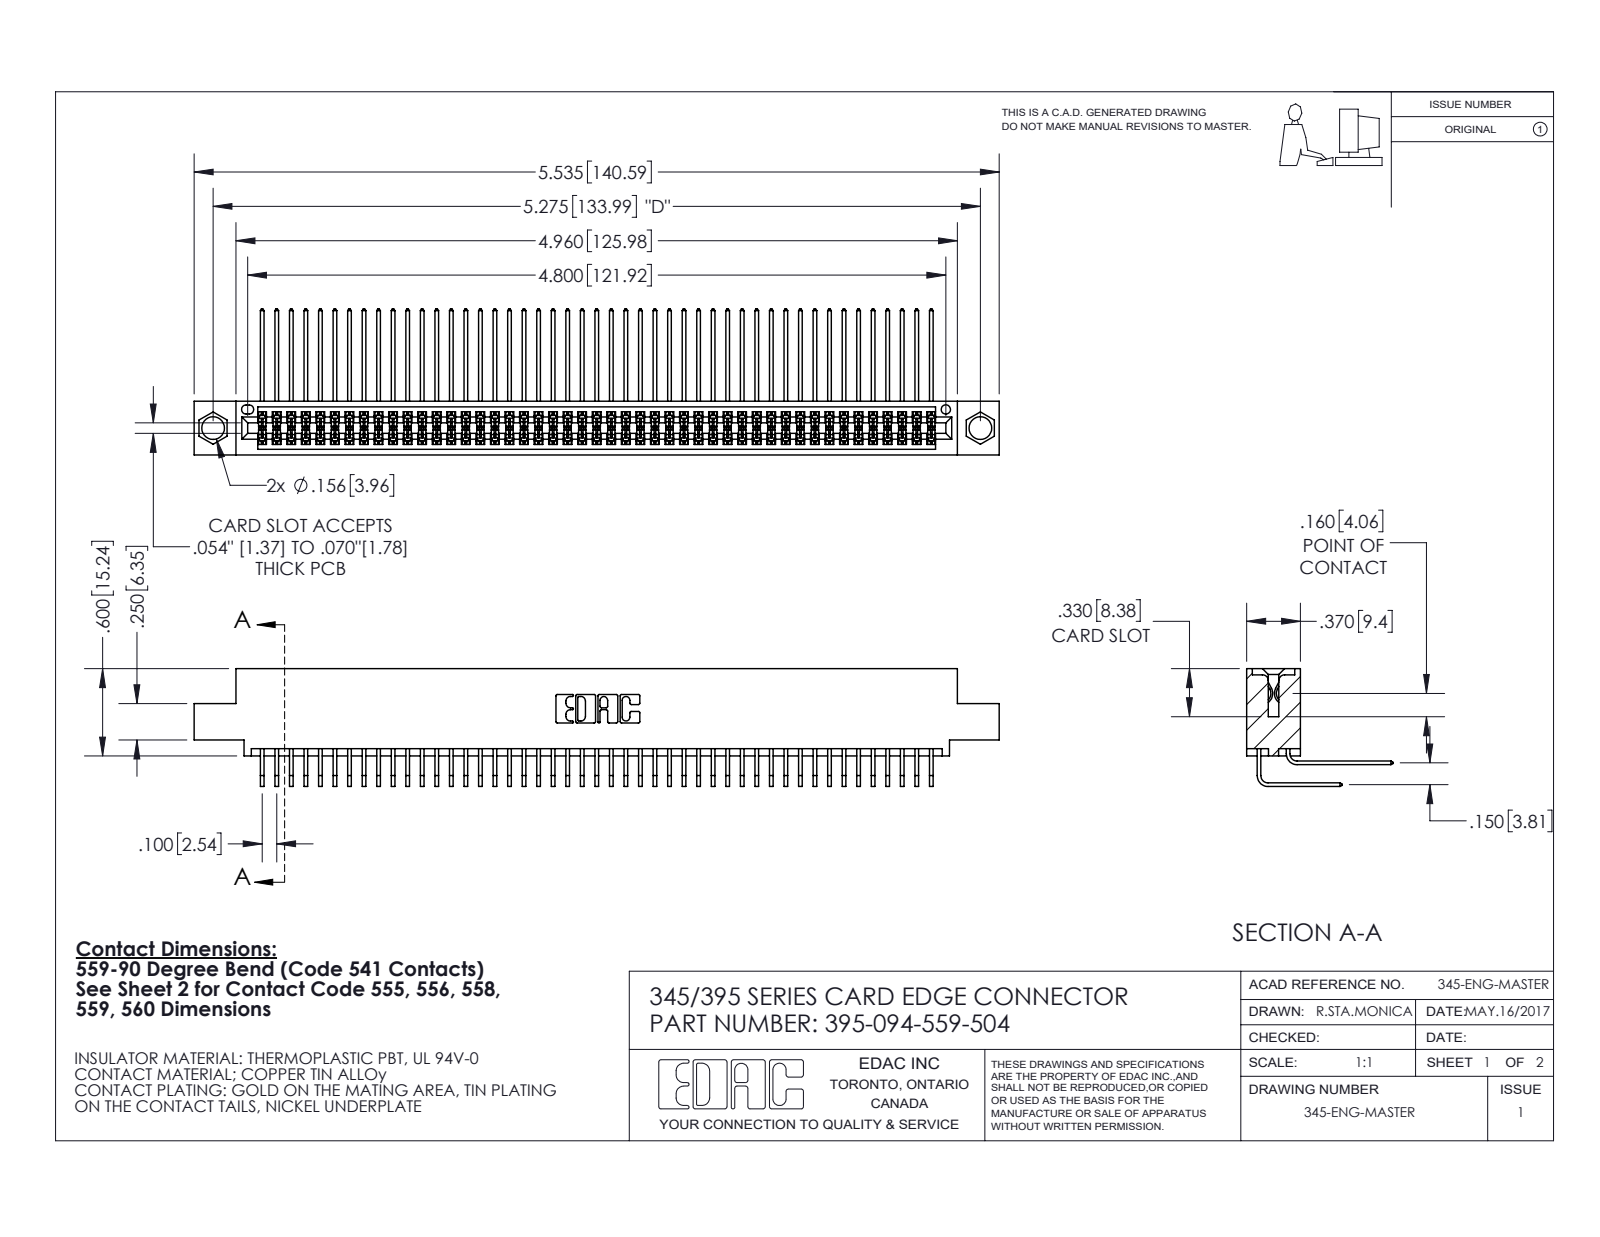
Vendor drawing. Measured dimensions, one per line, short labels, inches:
name: 395-094-559-504; 345 Part_0.110 Offset - 0.156 Dia-TI; 345-292-001_559 Tail - 2; 345-292-001_558 559 Tail - 1
written by: SolidWorks 2020 (CONFIG_CONTROL_DESIGN)
unit: in
bodies: 95 solids, 5032 faces (3388 planar, 1644 cylindrical, 0 other)
size: 5.535 × 1.005 × 0.809
volume: 0.858 in³; area: 36.24 in²
holes: 2× ⌀0.156, 1× ⌀0.064
rounds: 188× R0.006, 22× R0.01, 6× R0.007, 6× R0.031, 3× R0.026, 2× R0.014, 2× R0.019, 2× R0.022
face distances: 0.072, 0.298, 0.2, 0.37, 0.098, 0.272, 0.025, 0.225, 0.175, 0.15
hole spacings: 0.27, 5.039, 5.275
